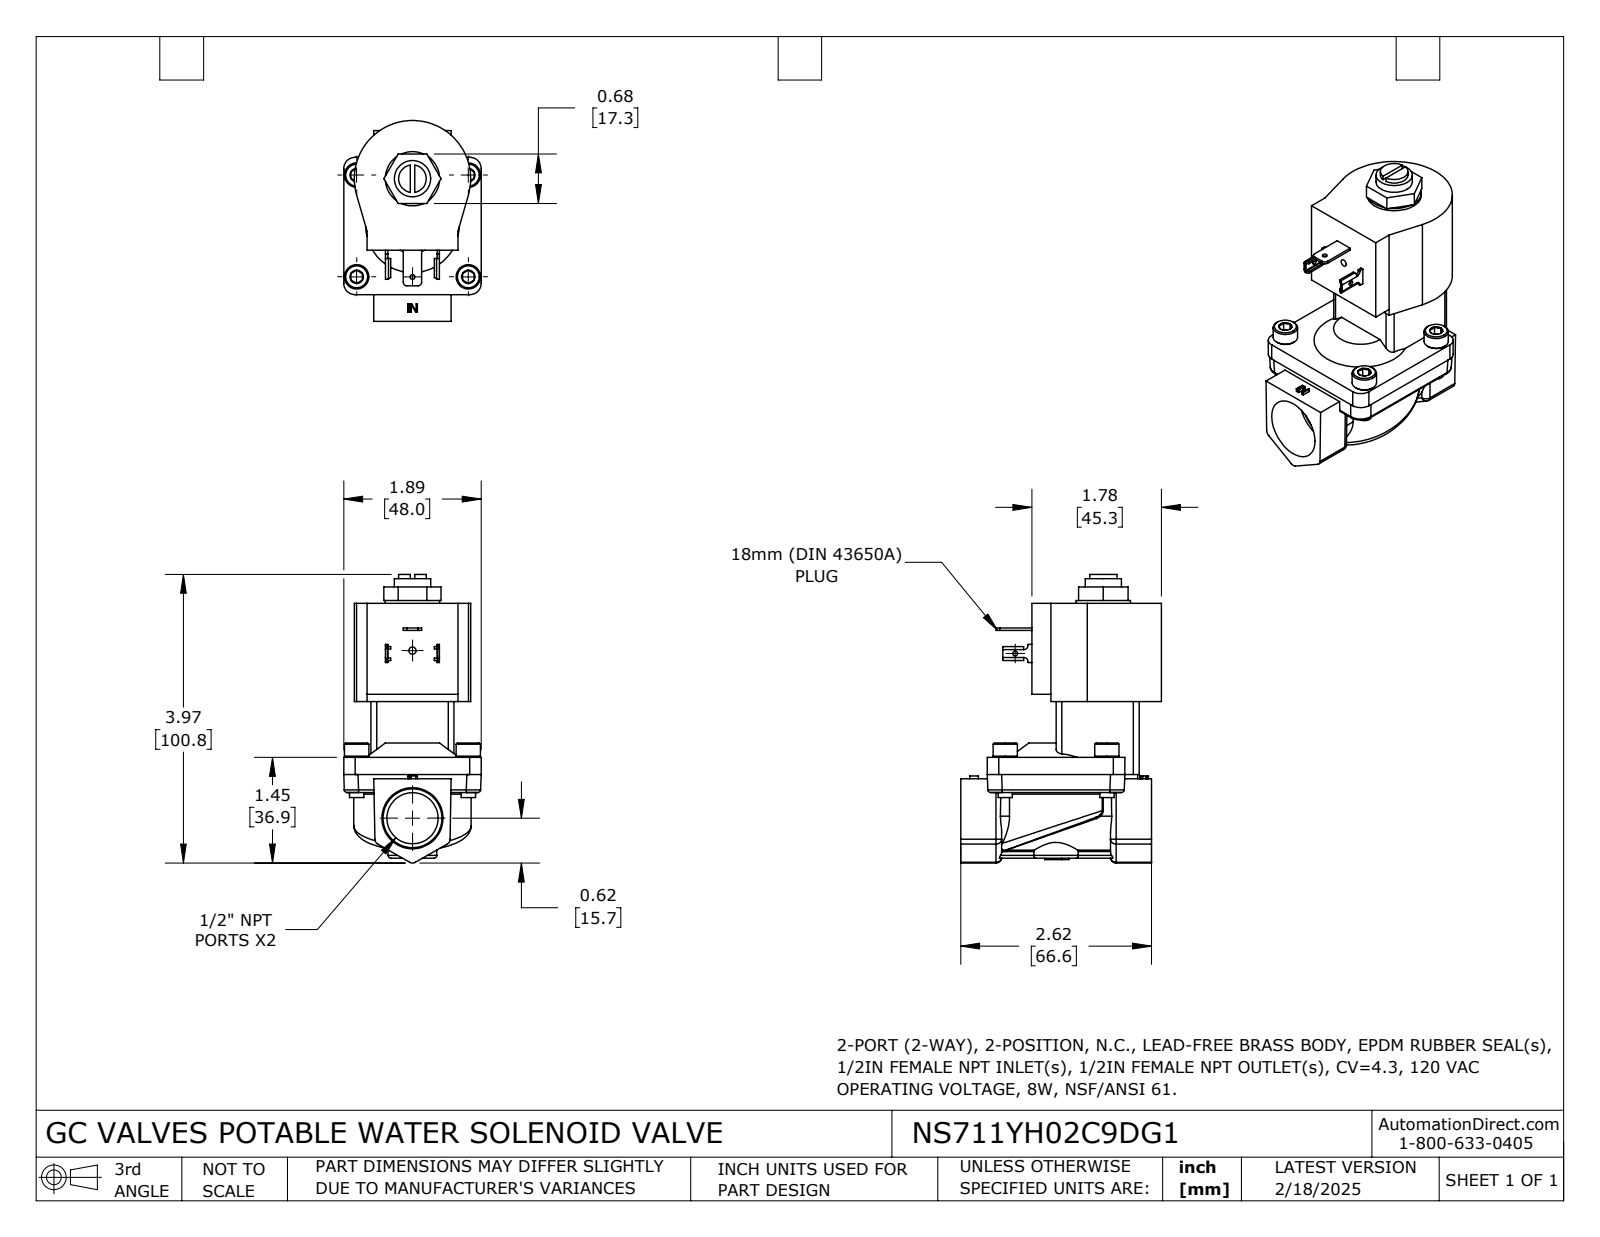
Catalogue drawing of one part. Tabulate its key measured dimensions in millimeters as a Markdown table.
| quantity | value |
| --- | --- |
| part name | NS711YH02C9DG1 |
| STEP written by | SolidWorks 2024 (CONFIG_CONTROL_DESIGN) |
| units | millimeters |
| bodies | 1 solid, 486 faces (270 planar, 113 cylindrical, 103 other) |
| overall size | 100.77 × 70.12 × 48 |
| volume | 127 340 mm³ |
| surface area | 26 767 mm² |
| round holes (diameter × count) | 1.68 × 1, 1.7 × 1, 2.53 × 1, 17.86 × 1, 30.48 × 1 |
| round bosses / shafts (diameter × count) | 8.5 × 4, 5 × 4, 18.95 × 1, 12.67 × 1, 9.65 × 1 |
| partial cylindrical surfaces (radius × count) | 2 × 15, 0.5 × 6, 1 × 6, 0.15 × 4, 1.04 × 4, 4 × 4, 5 × 4, 1.27 × 2 |
| main face-to-face distances | 19.5, 34.29, 53.79, 29, 22.04, 2.54, 31.75, 33.3, 37.44, 9.5 |
| hole center spacings | 34.29, 58.5 |
